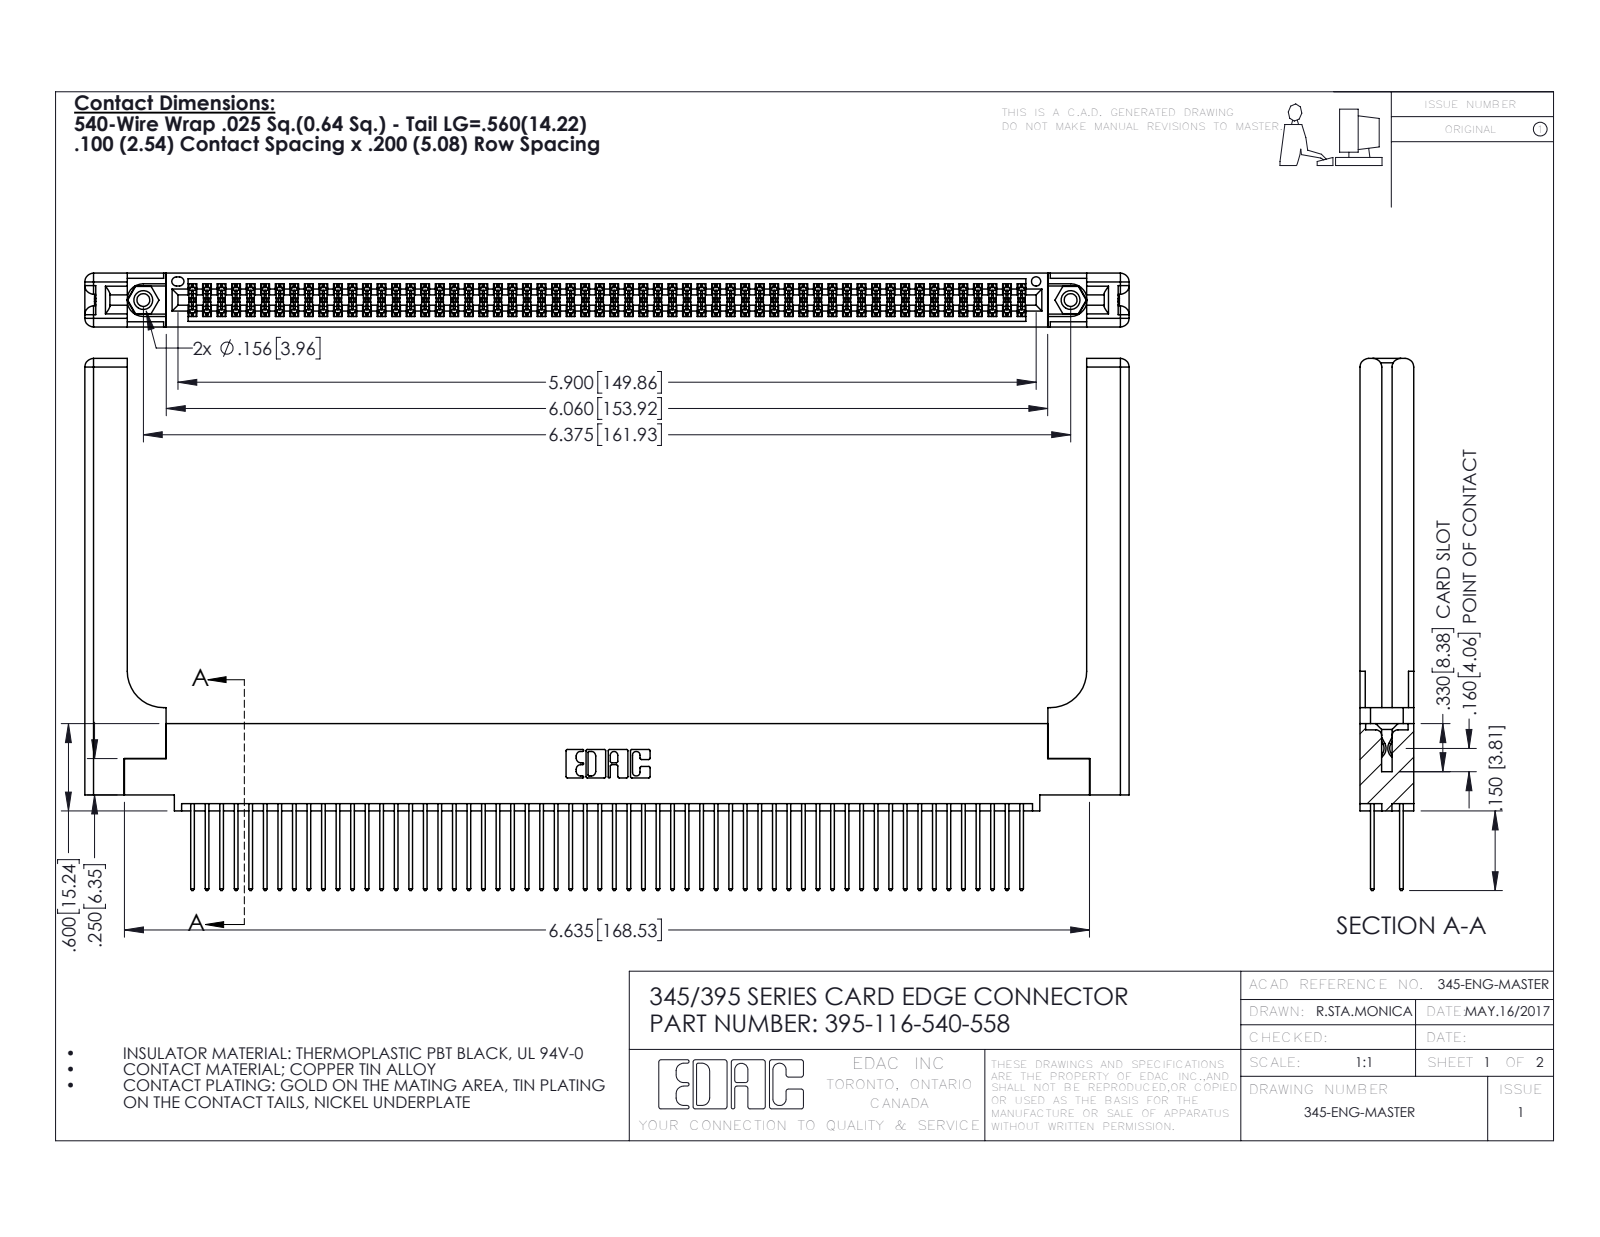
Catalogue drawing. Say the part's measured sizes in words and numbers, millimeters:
The part is named "345 Part_0.110 Offset - 0.156 Dia-TH; 395-116-540-558; 345-220-058_345-220-058; 345-292-001_345-293-140 (+1 more)". Its 3-D file was written by "SolidWorks 2016 (CONFIG_CONTROL_DESIGN)". It is 121 solids with 6186 faces: 4060 planar, 2066 cylindrical and 60 other. Overall it measures 182.3 by 92.9 by 9.4 millimeters. Its volume is 26 710 cubic millimeters and its surface area 34 450 square millimeters. Round holes: 2 of diameter 2.3, 2 of diameter 3.2, 2 of diameter 4, 1 of diameter 1.6. Round bosses or shafts: 2 of diameter 3.9. Partial cylindrical surfaces (rounded edges, fillets, slot ends): 174 of radius 0.2, 116 of radius 0.3, 22 of radius 0.3, 16 of radius 1.5, 6 of radius 0.2, 6 of radius 0.8, 3 of radius 0.7, 2 of radius 0.4. The main face-to-face distances are 1.8, 7.6, 9.4, 2.5, 6.9, 0.6, 5.1, 5.7, 4.4, 3.8. The hole center spacings are 6.9, 155.9, 161.9.
